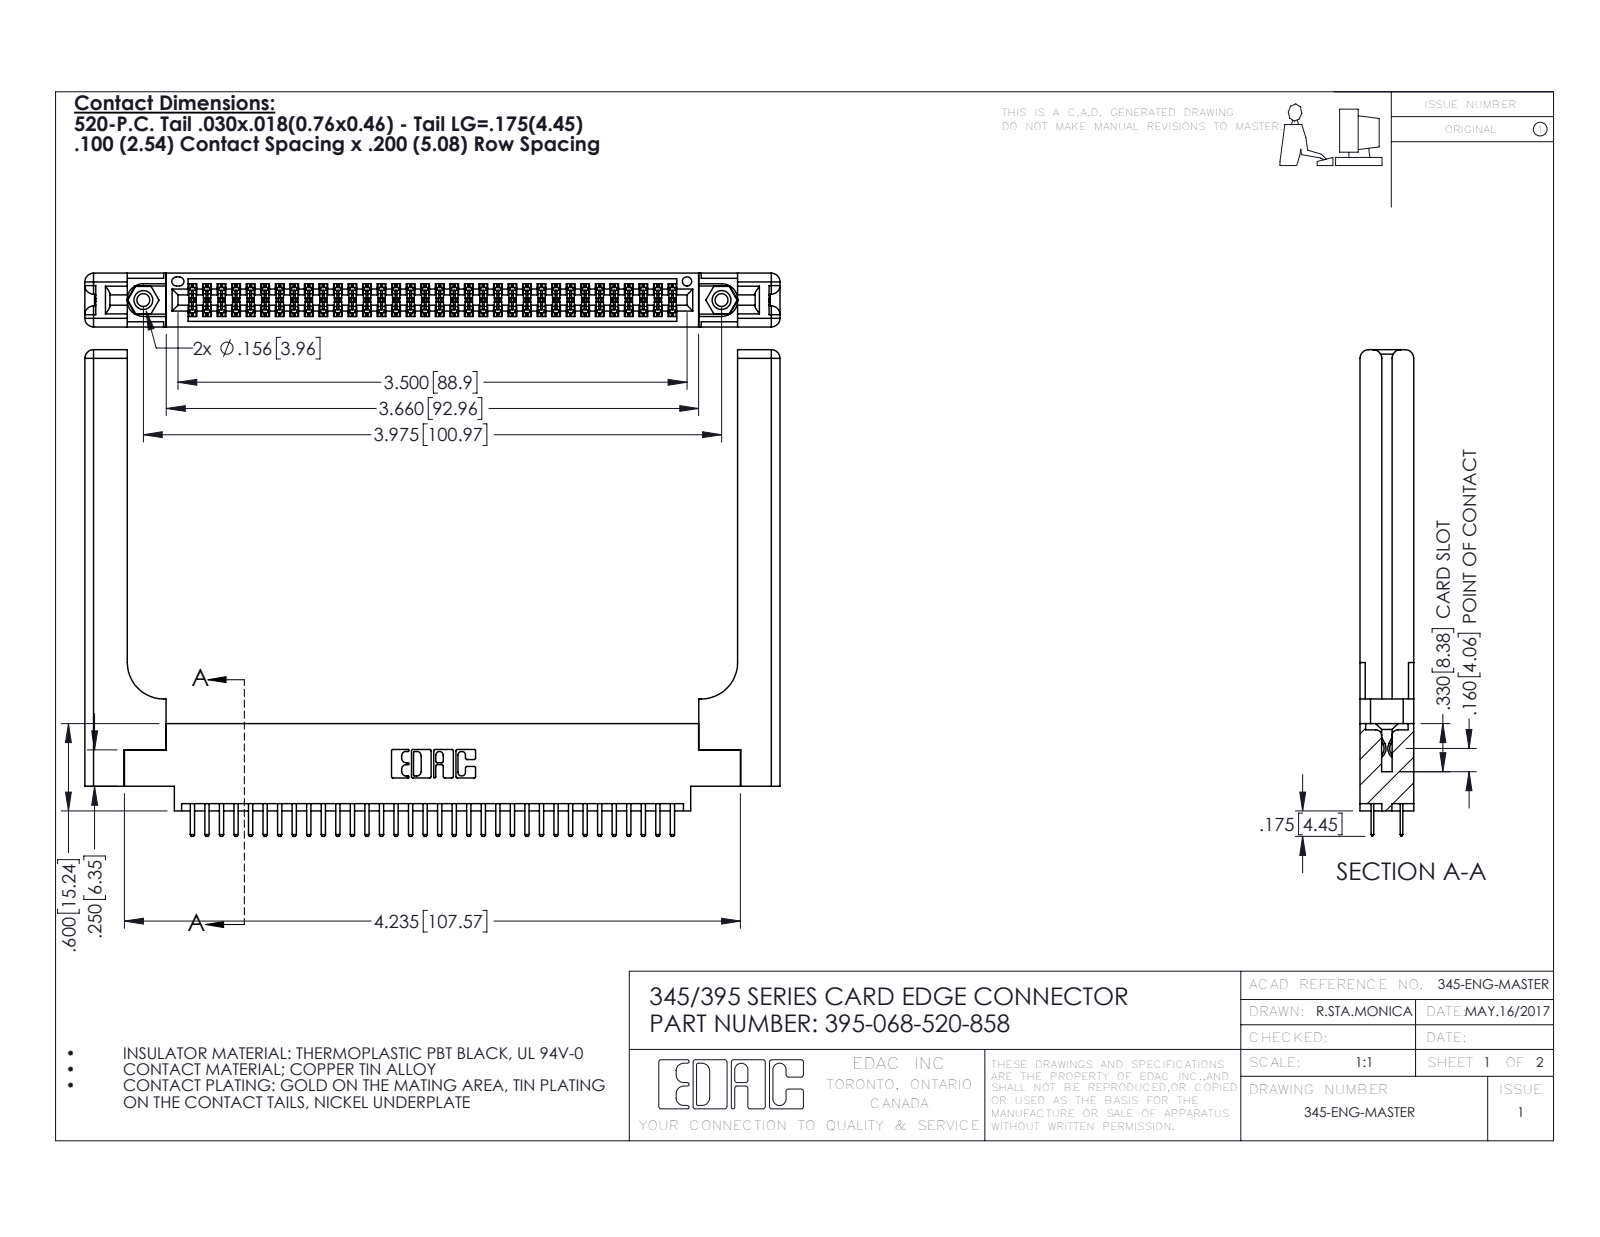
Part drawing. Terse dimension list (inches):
name: 345 Part_0.170 Offset - 0.156 Dia-TH; 345-292-001_345-293-120; 345-220-058_345-220-058; 395-068-520-858 (+1 more)
written by: SolidWorks 2016 (CONFIG_CONTROL_DESIGN)
unit: in
bodies: 73 solids, 4058 faces (2612 planar, 1386 cylindrical, 60 other)
size: 4.779 × 3.345 × 0.37
volume: 1.223 in³; area: 34.24 in²
holes: 2× ⌀0.089, 2× ⌀0.125, 2× ⌀0.156, 1× ⌀0.064
bosses: 2× ⌀0.155
rounds: 102× R0.006, 72× R0.01, 22× R0.01, 16× R0.06, 6× R0.007, 6× R0.031, 3× R0.026, 2× R0.014
face distances: 0.37, 0.072, 0.298, 0.2, 0.098, 0.272, 0.025, 0.225, 0.148, 0.15
hole spacings: 0.27, 3.74, 3.975
